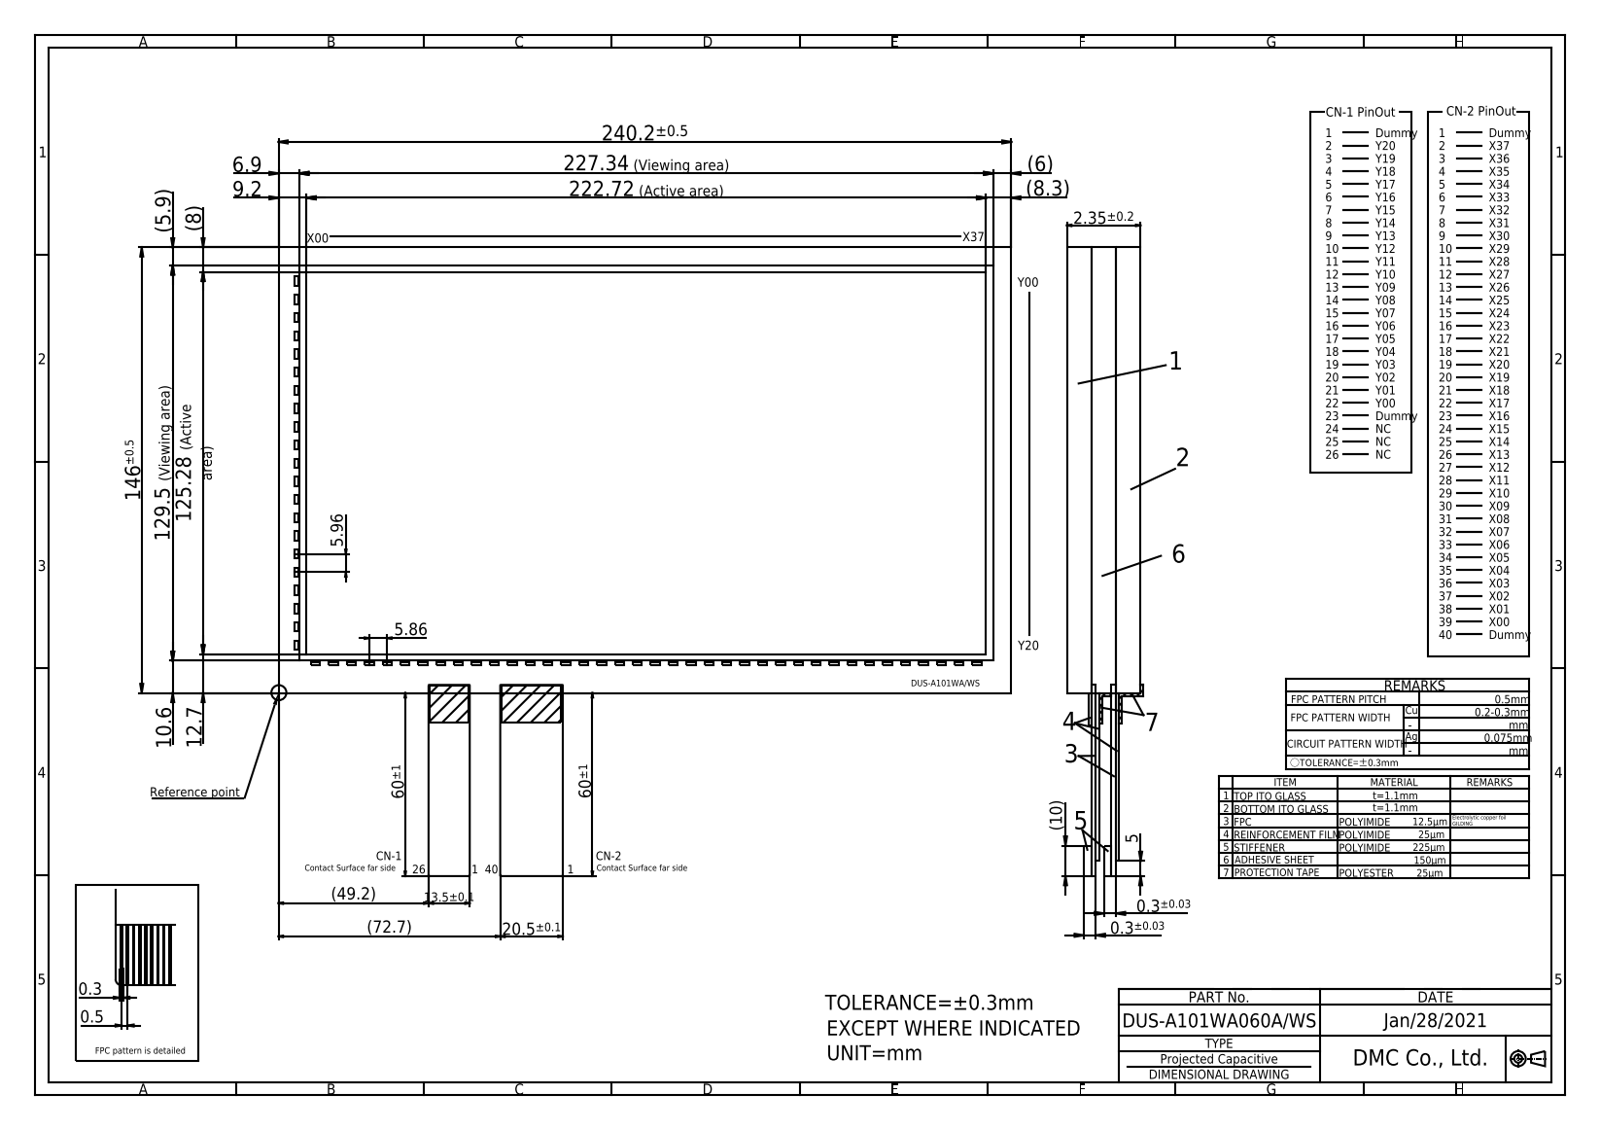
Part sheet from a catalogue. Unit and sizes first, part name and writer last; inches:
Units: inches
Overall size (bounding box): 13.239 × 9.26 × 0.093
Partial cylindrical surfaces — rounded edges, fillets, slot ends (radius × count): R0.008 ×4
Main face-to-face distances: 0.093, 0.045, 0.048, 0.049, 0.043, 0.044, 0.039, 0.089, 5.748, 9.457
Volume: 5.039 in³ · Surface area: 118.2 in²
Bodies: 1 solid, 302 faces (298 planar, 4 cylindrical, 0 other)
Part name (STEP PRODUCT): DUS-A101WA060A／WS
STEP written by: Autodesk Inventor 2020 (CONFIG_CONTROL_DESIGN)
